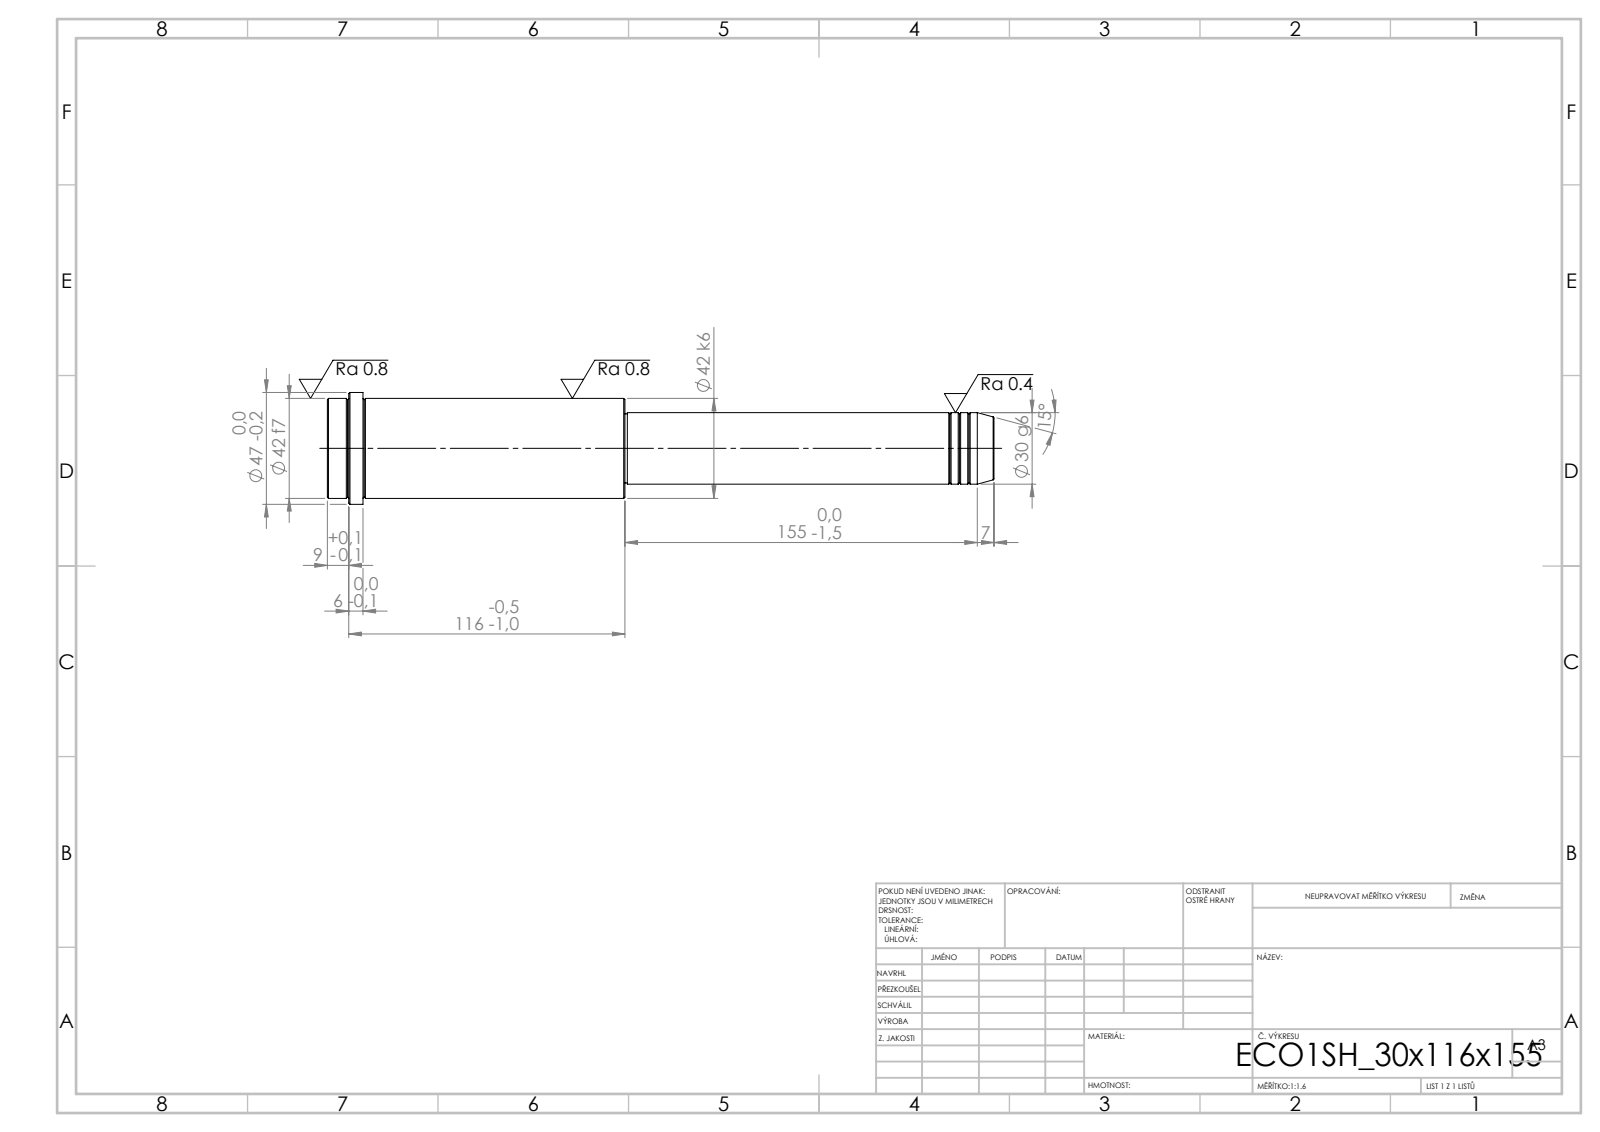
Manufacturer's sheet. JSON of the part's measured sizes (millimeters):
{"step_written_by": "SolidWorks 2019 (CONFIG_CONTROL_DESIGN)", "units": "millimeters", "bodies": {"solids": 1, "faces": 52, "planar": 6, "cylindrical": 16, "other": 30}, "overall_size": [280, 47, 47], "volume_mm3": 283936, "surface_area_mm2": 34736, "round_bosses_or_shafts": [[47, 1], [42, 1], [30, 1], [29, 1]], "face_to_face_distances": [125, 155, 280, 265, 110, 15, 271, 116, 6, 9]}
